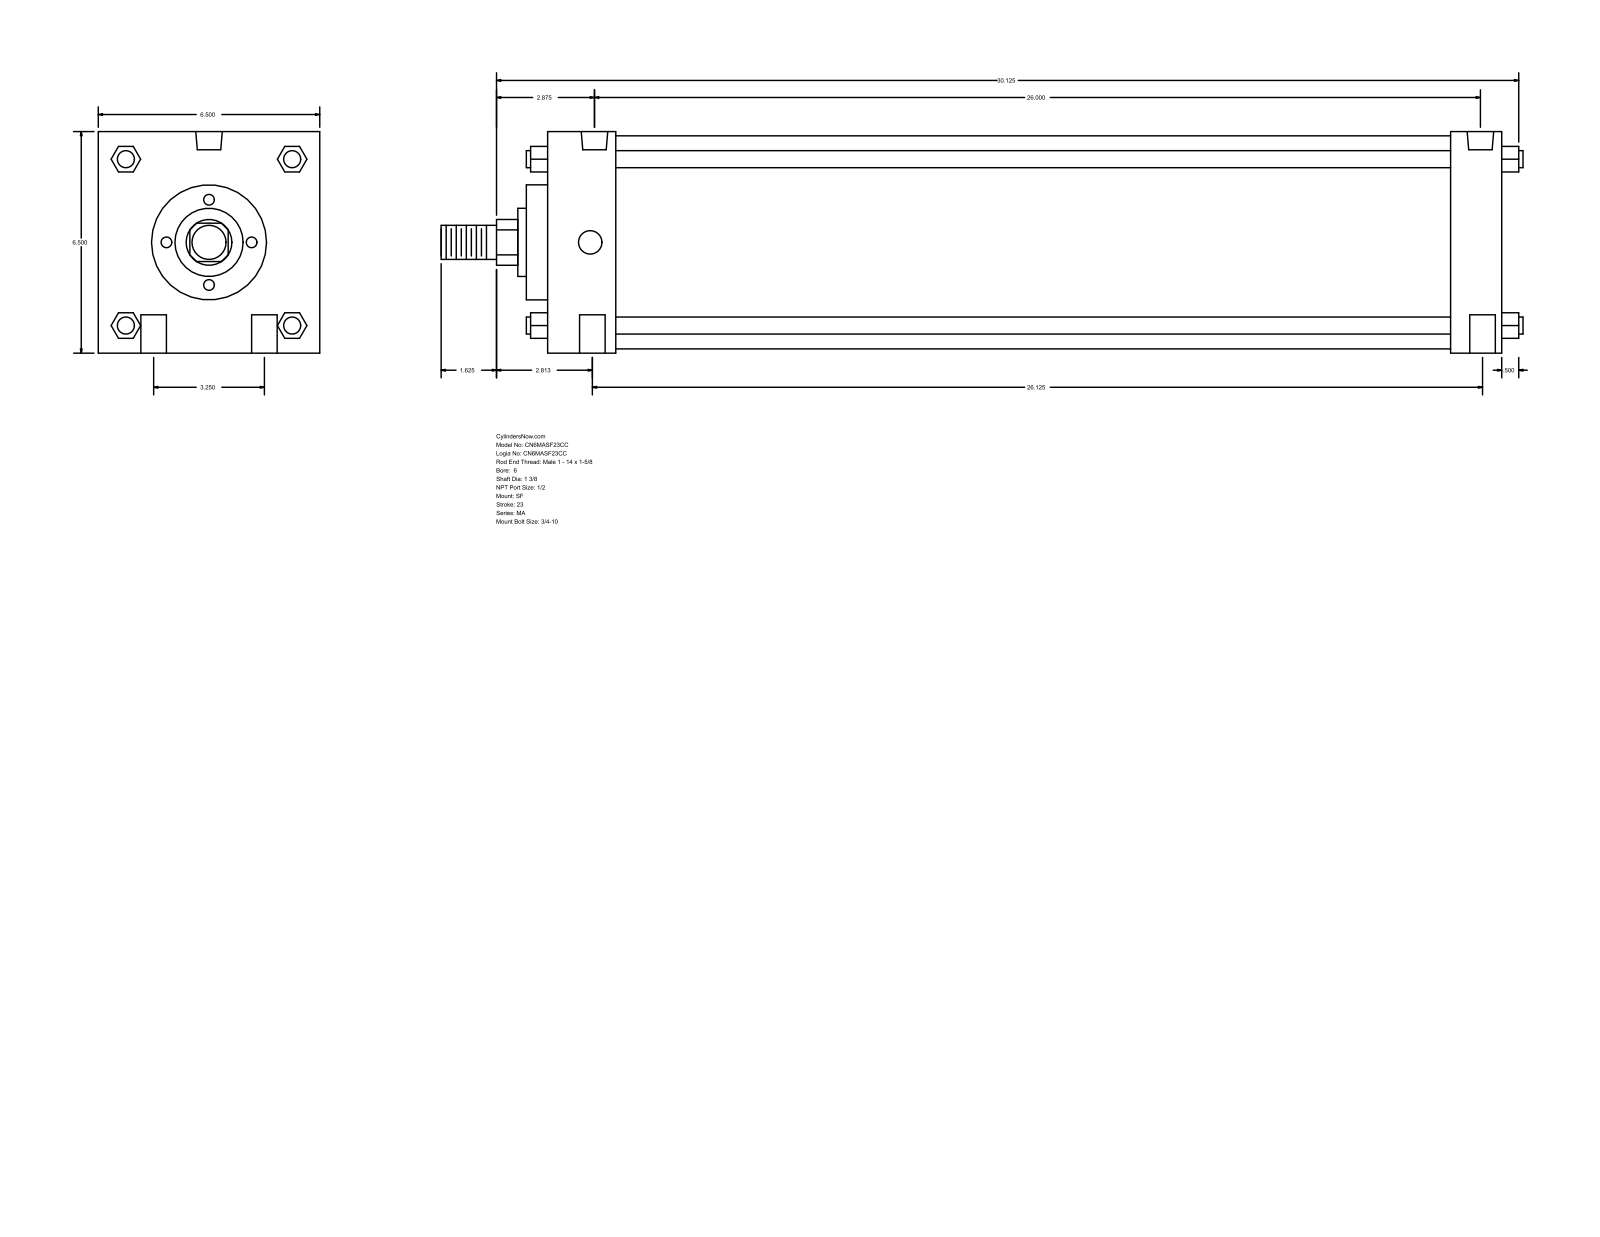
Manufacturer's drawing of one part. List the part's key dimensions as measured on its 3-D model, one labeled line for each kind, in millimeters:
Part name (STEP PRODUCT): MA_SF__0600_1.375
STEP written by: GSSL Pune (CONFIG_CONTROL_DESIGN)
Units: millimetres
Bodies: 0 solids, 126 faces (95 planar, 31 cylindrical, 0 other)
Overall size (bounding box): 806.45 × 165.1 × 165.1
Round holes (diameter × count): ⌀19.05 ×4, ⌀17.46 ×2, ⌀19.77 ×2
Round bosses / shafts (diameter × count): ⌀12.7 ×4, ⌀158.75 ×1, ⌀85.72 ×1, ⌀50.8 ×1, ⌀34.92 ×1, ⌀25.4 ×1
Partial cylindrical surfaces — rounded edges, fillets, slot ends (radius × count): R17.06 ×1
Main face-to-face distances: 165.1, 711.2, 673.1, 50.8, 38.1, 622.3, 660.4, 66.67, 15.87, 727.07
Hole centre spacings: 41.3, 663.27, 82.54, 663.57, 668.68, 660.39, 660.4
